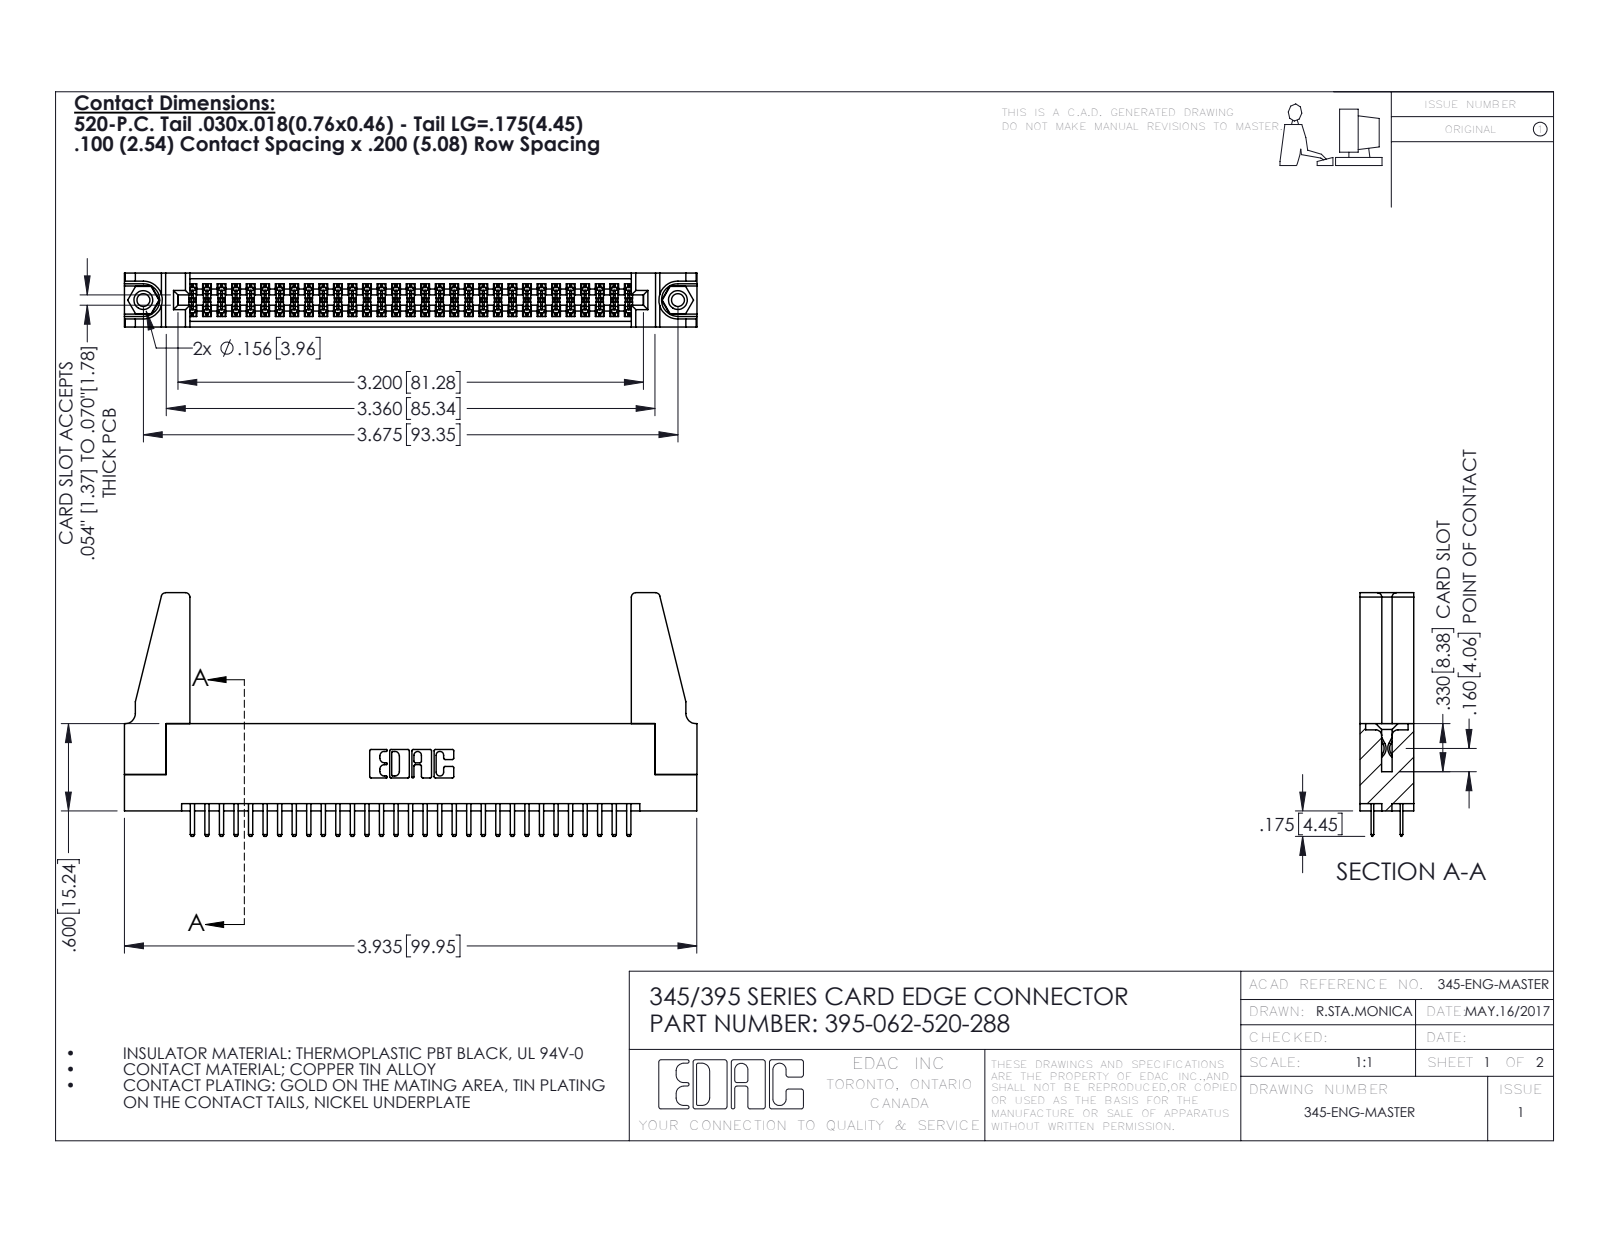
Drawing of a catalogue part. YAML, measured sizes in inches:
part_name: "345-292-001_345-293-120; 345 Part_Flush Mounting Lugs - 0.156 Dia-TH; 395-062-520-288; 345-220-078_345-220-088 (+1 more)"
step_written_by: "SolidWorks 2016 (CONFIG_CONTROL_DESIGN)"
units: inches
bodies: {solids: 67, faces: 3598, planar: 2322, cylindrical: 1260, other: 16}
overall_size: [3.936, 1.675, 0.37]
volume: 0.783
surface_area: 26.37
round_holes:
  - {diameter: 0.089, count: 2}
  - {diameter: 0.125, count: 2}
  - {diameter: 0.156, count: 2}
  - {diameter: 0.064, count: 1}
round_bosses_or_shafts:
  - {diameter: 0.155, count: 2}
partial_cylinders:
  - {radius: 0.006, count: 93}
  - {radius: 0.01, count: 66}
  - {radius: 0.01, count: 22}
  - {radius: 0.03, count: 8}
  - {radius: 0.007, count: 6}
  - {radius: 0.031, count: 6}
  - {radius: 0.026, count: 3}
  - {radius: 0.014, count: 2}
face_to_face_distances: [0.072, 0.298, 0.37, 0.2, 0.098, 0.272, 0.025, 0.225, 0.022, 0.072]
hole_center_spacings: [0.27, 3.44, 3.675]
